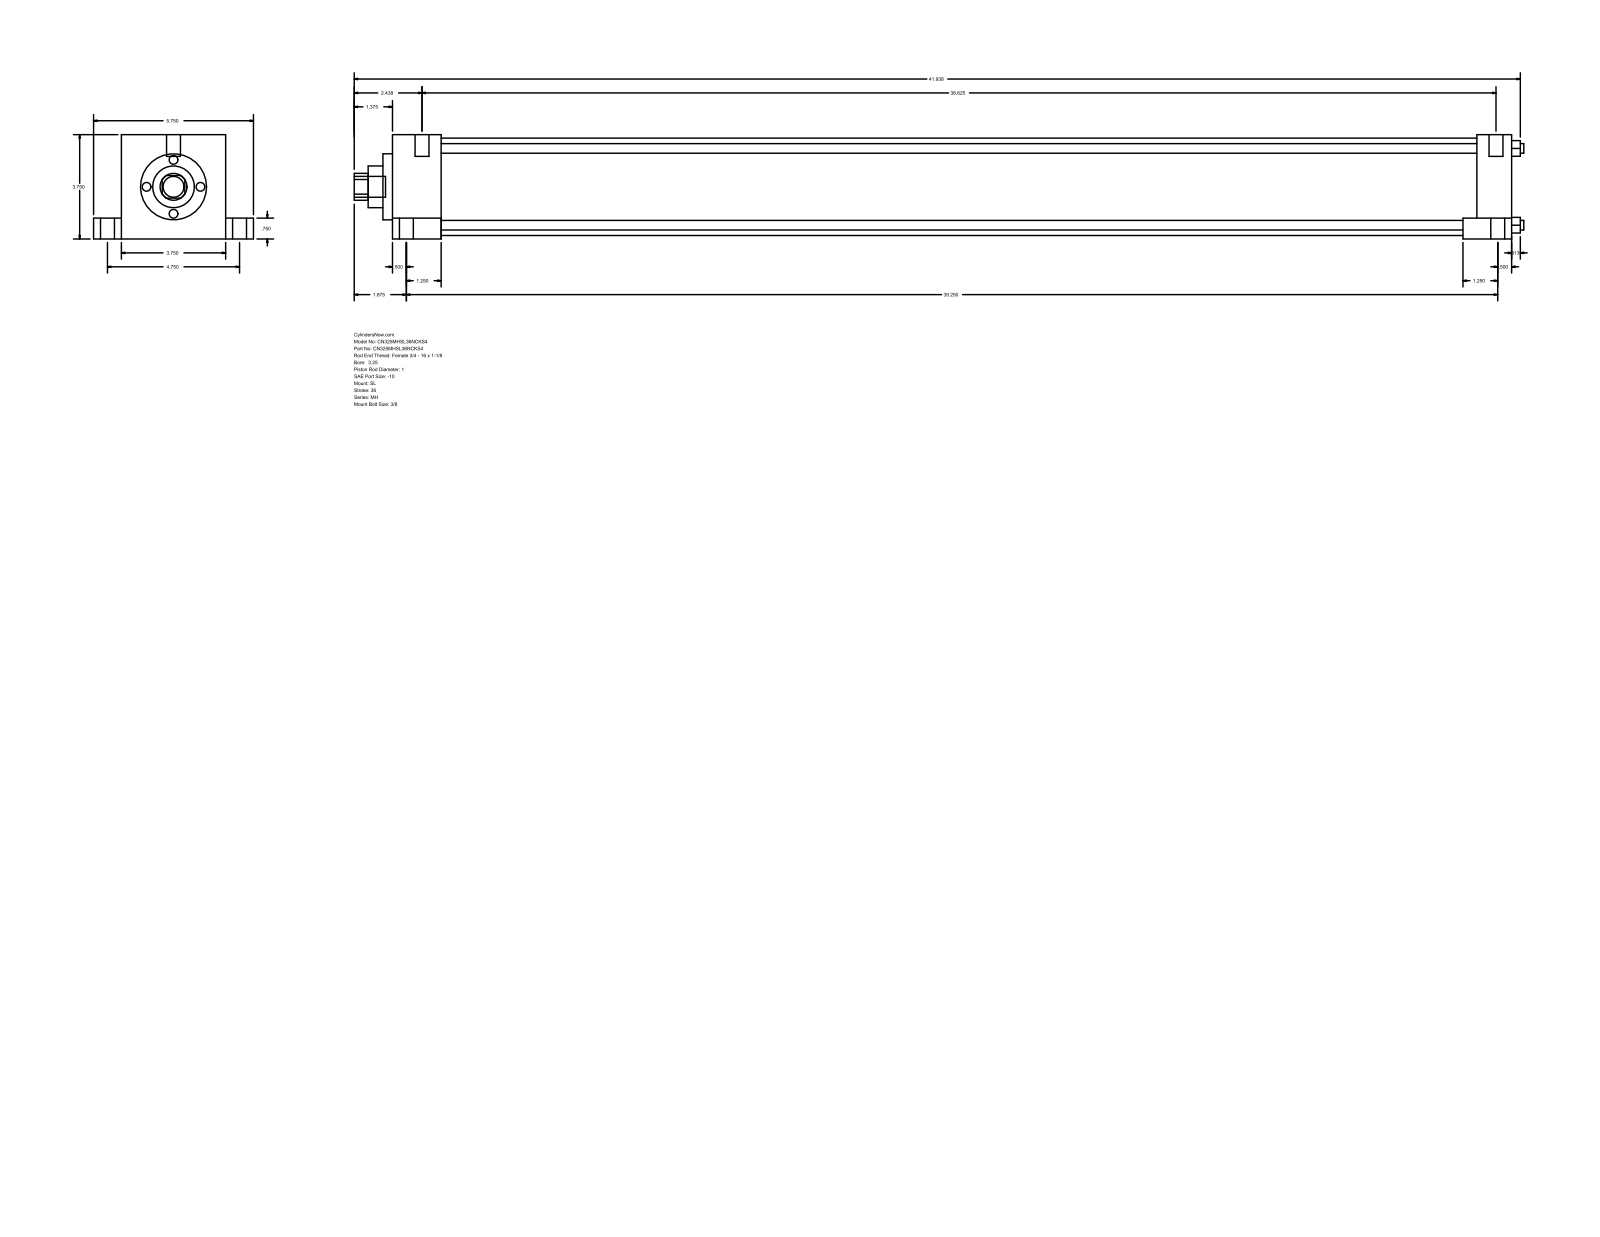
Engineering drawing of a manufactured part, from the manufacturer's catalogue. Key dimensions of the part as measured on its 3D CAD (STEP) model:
Part name (STEP PRODUCT): MH_SL__0325_1
STEP written by: GSSL Pune (CONFIG_CONTROL_DESIGN)
Units: millimetres
Bodies: 0 solids, 110 faces (77 planar, 33 cylindrical, 0 other)
Overall size (bounding box): 1068.39 × 146.05 × 95.25
Round holes (diameter × count): ⌀8.76 ×4, ⌀25.4 ×1, ⌀38.1 ×1, ⌀60.33 ×1, ⌀88.9 ×1
Round bosses / shafts (diameter × count): ⌀12.7 ×6, ⌀19.05 ×5, ⌀5.56 ×4
Partial cylindrical surfaces — rounded edges, fillets, slot ends (radius × count): R12.29 ×1
Main face-to-face distances: 95.24, 1022.36, 44.46, 977.9, 25.41, 120.65, 19.05, 76.19, 990.61, 946.15
Hole centre spacings: 49.57, 70.1, 99.14
